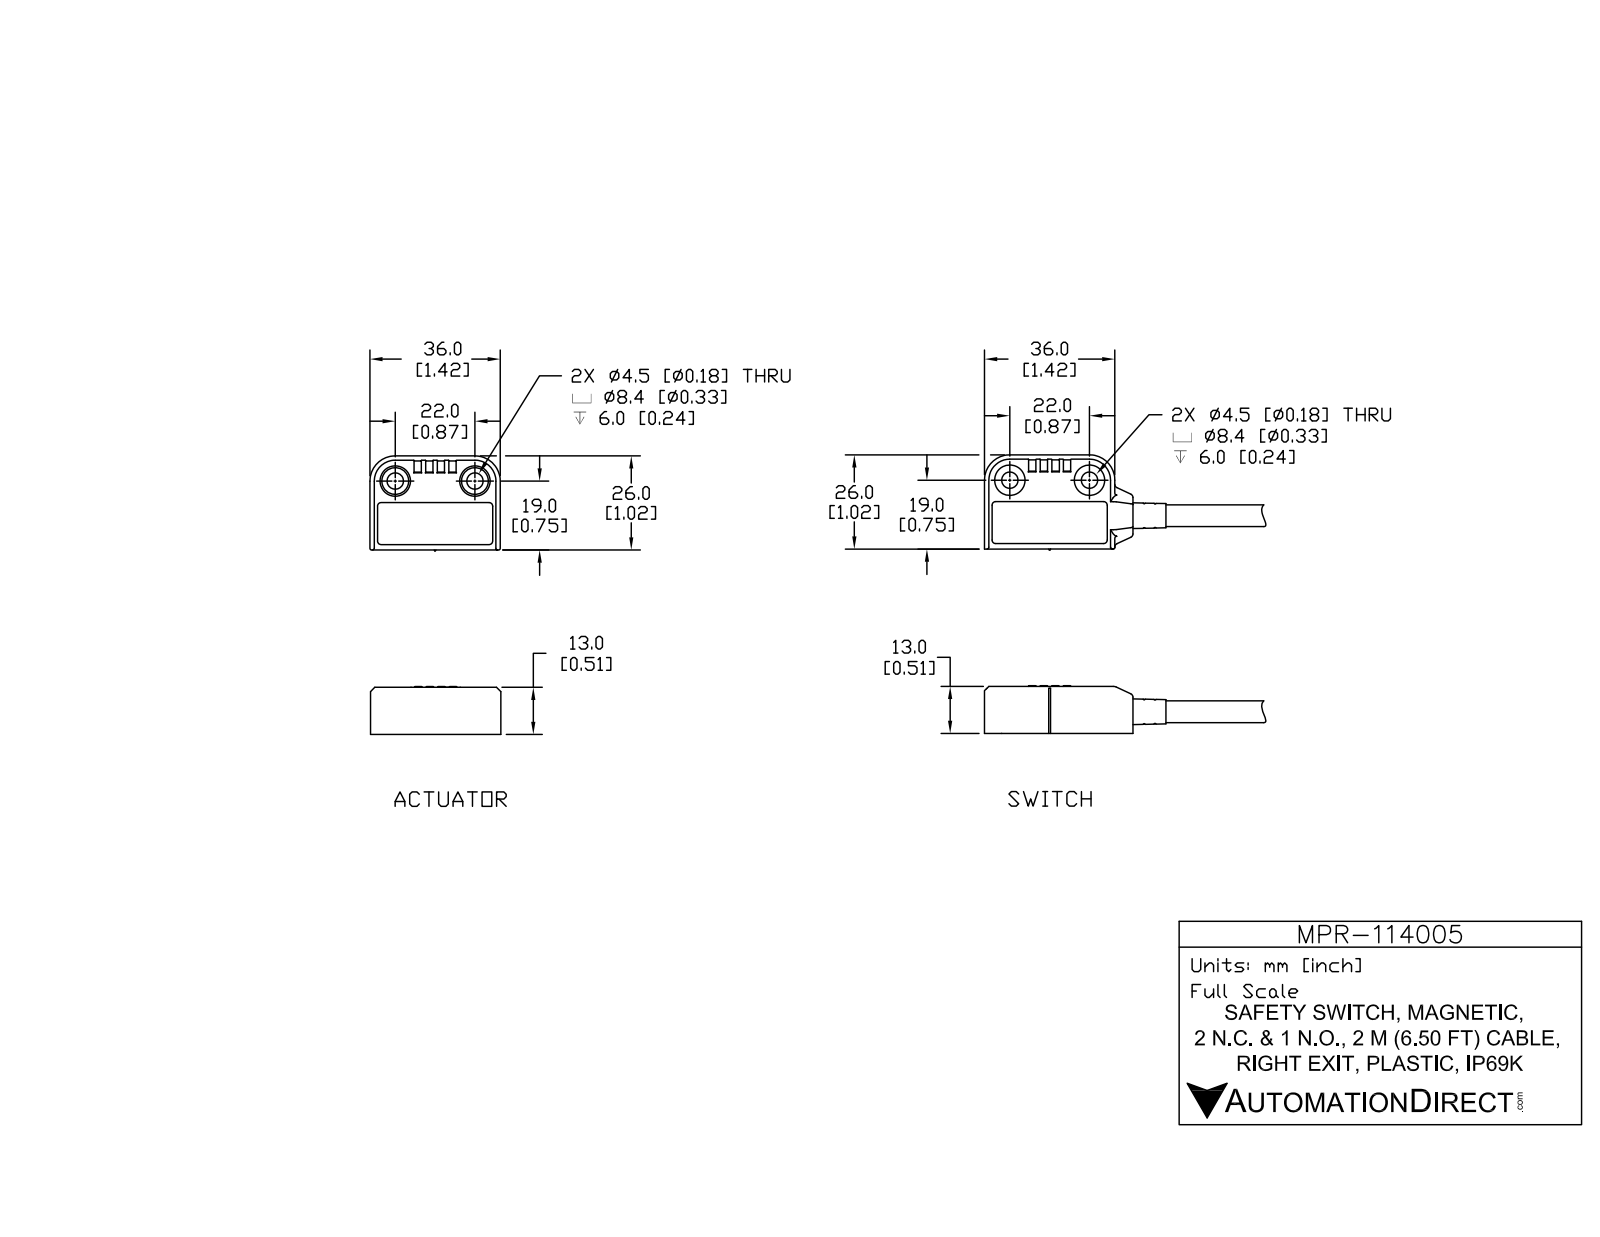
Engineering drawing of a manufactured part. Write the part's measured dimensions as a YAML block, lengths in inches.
part_name: "MPR-114005_1; MPR-114005_2; MPR-114005"
step_written_by: "SolidWorks 2017 (AUTOMOTIVE_DESIGN)"
units: inches
bodies: {solids: 9, faces: 1110, planar: 486, cylindrical: 325, other: 299}
overall_size: [7.658, 2.087, 0.528]
volume: 1.059
surface_area: 29.57
round_holes:
  - {diameter: 0.177, count: 4}
  - {diameter: 0.331, count: 4}
  - {diameter: 0.195, count: 2}
  - {diameter: 0.197, count: 1}
  - {diameter: 0.232, count: 1}
  - {diameter: 0.276, count: 1}
round_bosses_or_shafts:
  - {diameter: 0.079, count: 3}
  - {diameter: 0.197, count: 2}
  - {diameter: 0.091, count: 2}
  - {diameter: 0.339, count: 1}
  - {diameter: 0.299, count: 1}
  - {diameter: 0.28, count: 1}
  - {diameter: 0.236, count: 1}
partial_cylinders:
  - {radius: 0.02, count: 85}
  - {radius: 0.008, count: 30}
  - {radius: 0.012, count: 28}
  - {radius: 0.004, count: 17}
  - {radius: 0.039, count: 13}
  - {radius: 0.169, count: 4}
  - {radius: 0.201, count: 4}
  - {radius: 0.276, count: 4}
face_to_face_distances: [0.055, 0.461, 0.39, 0.453, 0.047, 1.063, 0.059, 0.094, 0.445, 0.031]
hole_center_spacings: [0.866, 0.445, 0.974, 1.091, 1.393, 1.535, 1.763, 0.396]
